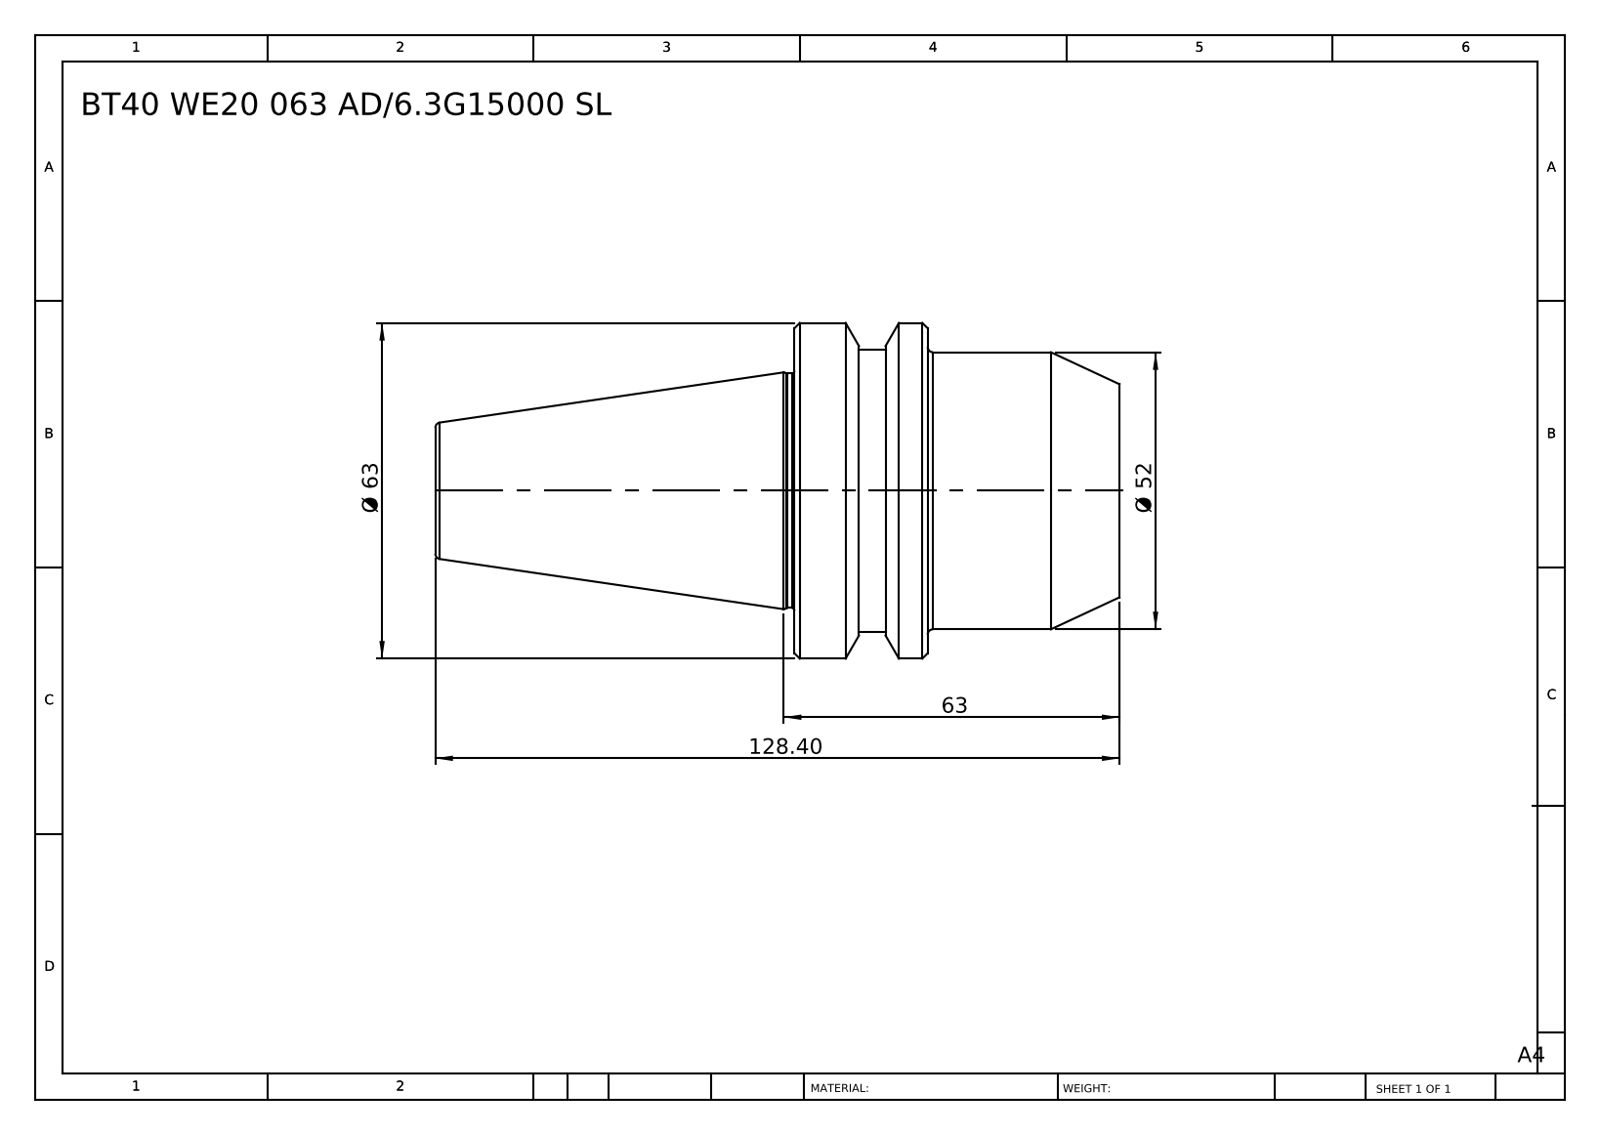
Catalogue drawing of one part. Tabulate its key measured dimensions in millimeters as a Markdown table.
| quantity | value |
| --- | --- |
| part name | BT40 WE20 063 AD-6.3G15000 SL |
| STEP written by | SolidWorks 2014 (CONFIG_CONTROL_DESIGN) |
| units | millimeters |
| bodies | 1 solid, 38 faces (6 planar, 10 cylindrical, 22 other) |
| overall size | 128.4 × 63 × 63 |
| volume | 209 015 mm³ |
| surface area | 23 227 mm² |
| round bosses / shafts (diameter × count) | 63 × 1, 53 × 1, 52 × 1, 44 × 1 |
| main face-to-face distances | 61, 36, 25, 128.4, 92.4, 67.4, 48.9, 12.9, 12.1, 79.5 |
